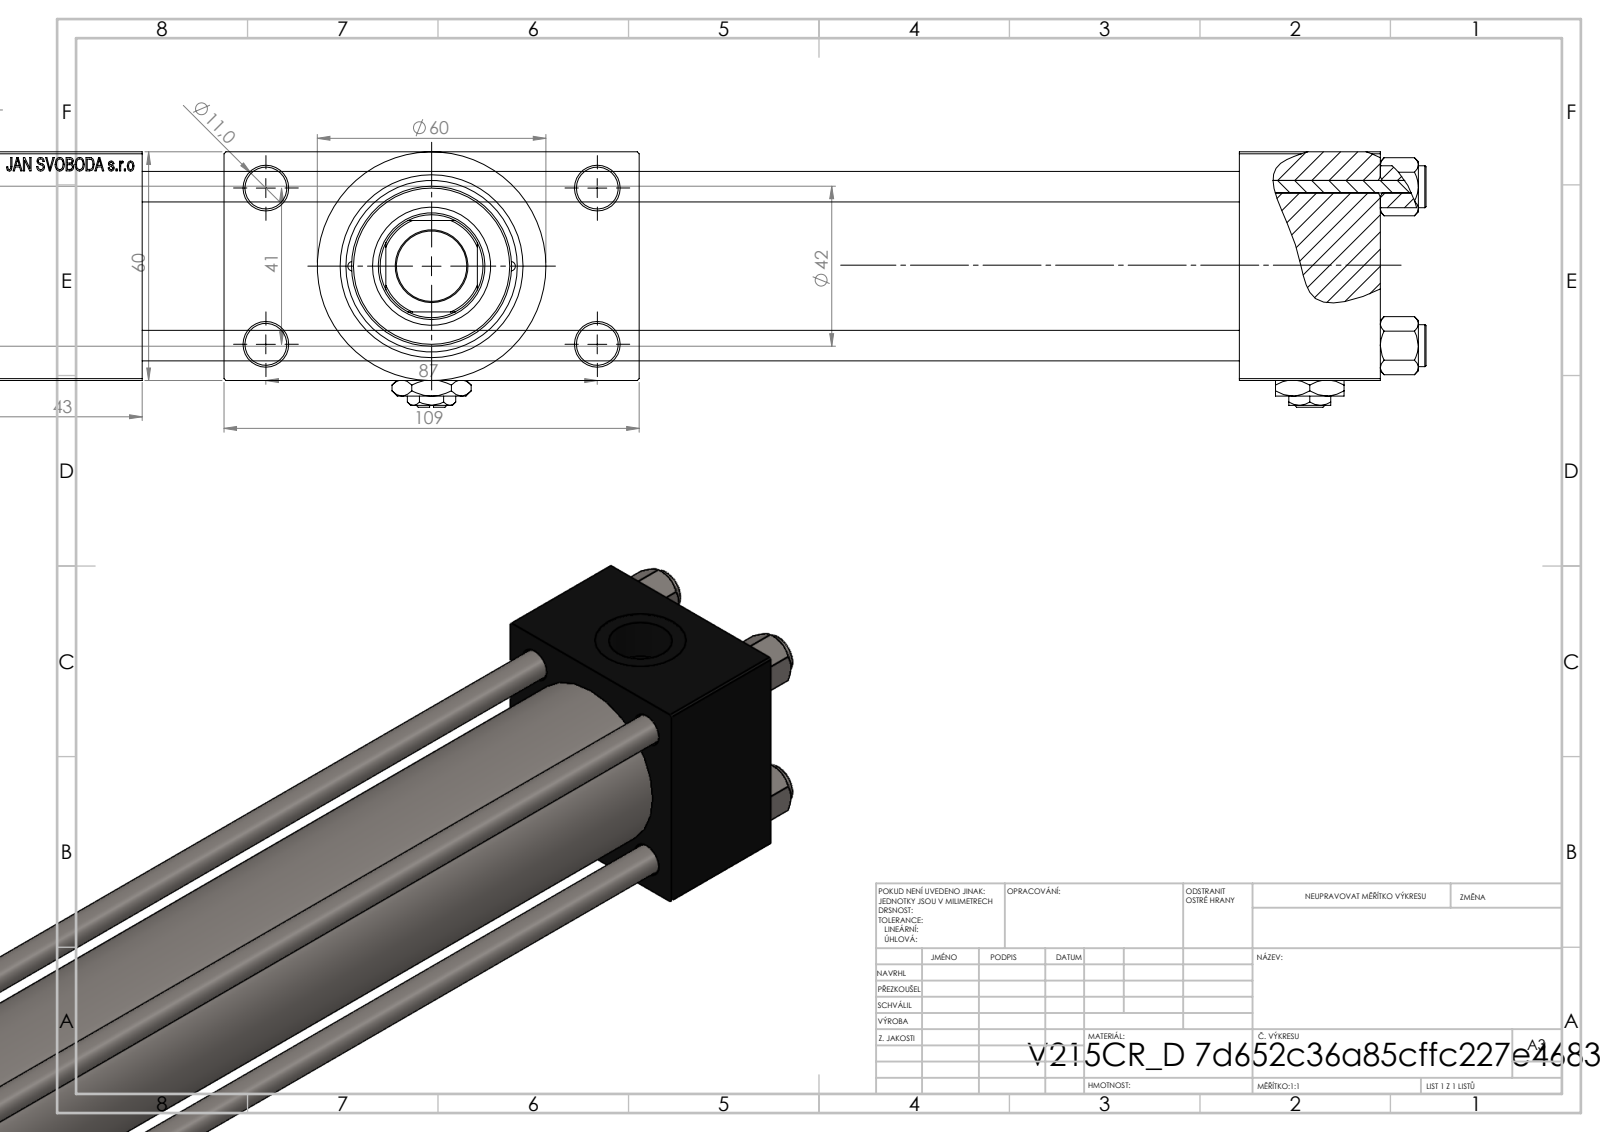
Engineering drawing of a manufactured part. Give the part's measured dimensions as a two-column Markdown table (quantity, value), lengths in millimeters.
| quantity | value |
| --- | --- |
| part name | V215_VC_A; V215CR_D_Body; V215CR_D_TYCINKA; Zatka_pro_OIL_PORT (+2 more) |
| STEP written by | SolidWorks 2019 (CONFIG_CONTROL_DESIGN) |
| units | millimeters |
| bodies | 12 solids, 1168 faces (526 planar, 100 cylindrical, 542 other) |
| overall size | 415 × 109 × 67 |
| volume | 813 246 mm³ |
| surface area | 235 027 mm² |
| round holes (diameter × count) | 8 × 4, 11 × 4, 2.5 × 2, 7 × 2, 16.66 × 2, 24 × 2, 18.5 × 1, 28 × 1, 31 × 1, 40 × 1, 45 × 1 |
| round bosses / shafts (diameter × count) | 11 × 4, 60 × 1, 46 × 1, 42 × 1 |
| partial cylindrical surfaces (radius × count) | 13.5 × 1 |
| main face-to-face distances | 60, 24.5, 84.5, 288, 37, 325, 368, 331, 43, 109 |
| hole center spacings | 20.85, 22.65, 29.49, 30.62, 41.7, 46.53, 47.15, 48.09 |
